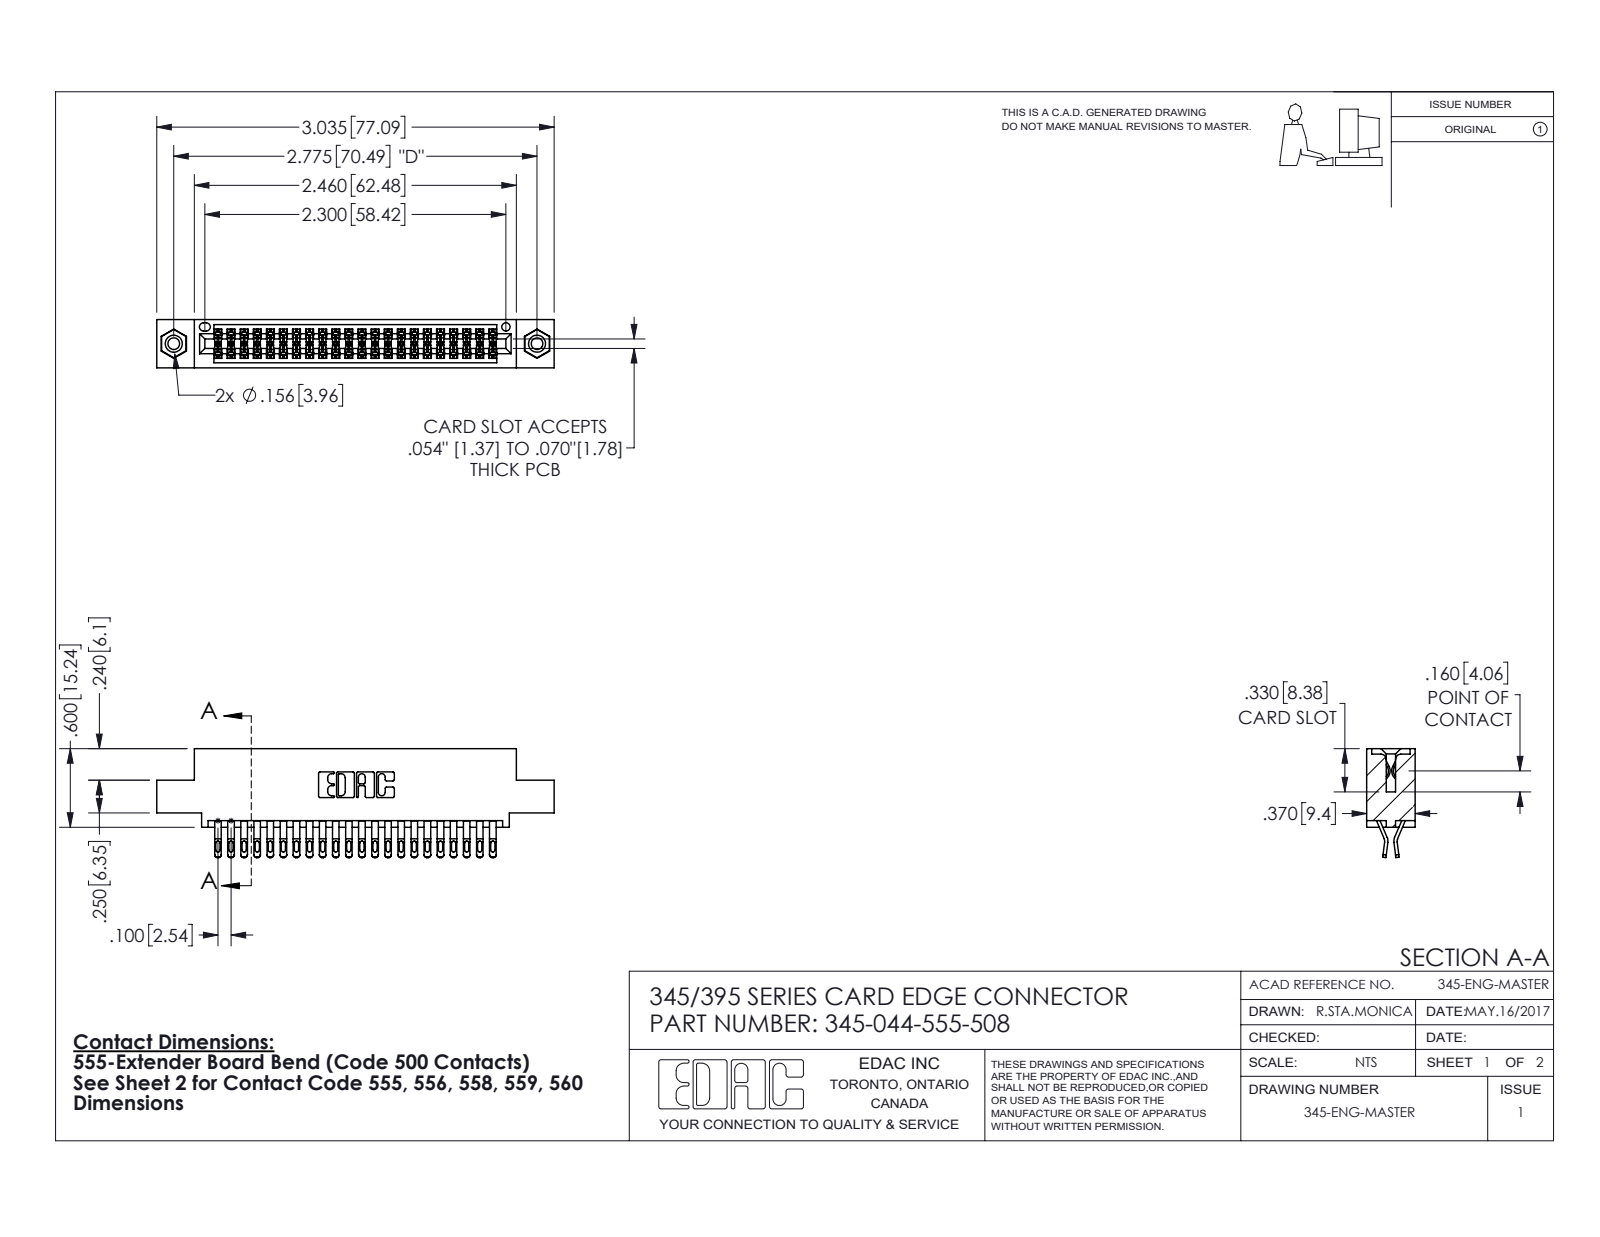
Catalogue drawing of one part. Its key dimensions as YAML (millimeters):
part_name: "345-044-555-508; 345-250-001_345-250-003-102; 345-292-001_555 Tail; 345 Part_0.110 Offset - 0.156 Dia-TI"
step_written_by: "SolidWorks 2016 (CONFIG_CONTROL_DESIGN)"
units: millimeters
bodies: {solids: 47, faces: 2654, planar: 1480, cylindrical: 1158, other: 16}
overall_size: [77.1, 21.1, 9.4]
volume: 7360
surface_area: 11030
round_holes:
  - {diameter: 2.3, count: 2}
  - {diameter: 3.2, count: 2}
  - {diameter: 4, count: 2}
  - {diameter: 1.6, count: 1}
round_bosses_or_shafts:
  - {diameter: 3.9, count: 2}
partial_cylinders:
  - {radius: 0.4, count: 110}
  - {radius: 0.5, count: 88}
  - {radius: 0.2, count: 66}
  - {radius: 0.3, count: 22}
  - {radius: 0.2, count: 6}
  - {radius: 0.8, count: 6}
  - {radius: 0.7, count: 3}
  - {radius: 0.3, count: 2}
face_to_face_distances: [1.8, 7.6, 5.1, 9.4, 0.6, 2.5, 6.9, 5.7, 4.4, 3.8]
hole_center_spacings: [6.9, 64.5, 70.5]
